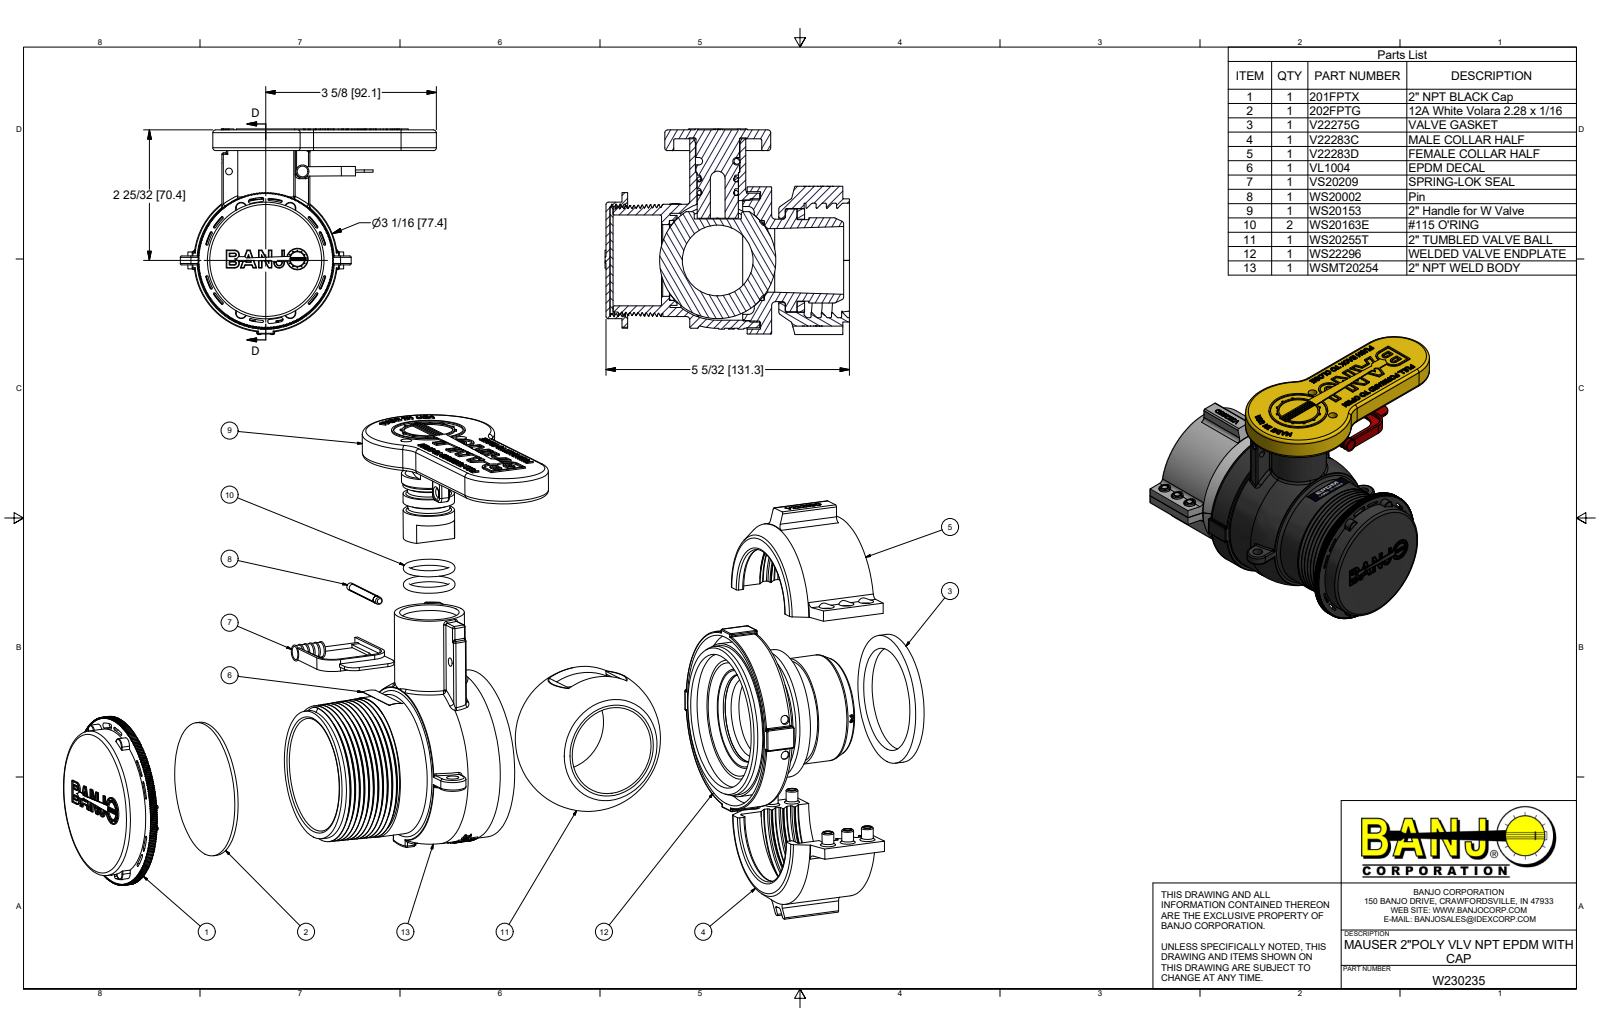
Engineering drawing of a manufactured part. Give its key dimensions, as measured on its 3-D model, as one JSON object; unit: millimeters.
{"part_name": "W230235; WSMT20254; WSMT20254X; V22275G (+8 more)", "step_written_by": "Autodesk Inventor 2018 (AUTOMOTIVE_DESIGN)", "units": "millimeters", "bodies": {"solids": 16, "faces": 3810, "planar": 1882, "cylindrical": 936, "other": 992}, "overall_size": [1020.5, 138.2, 110.9], "volume_mm3": 320000, "surface_area_mm2": 326900, "round_holes": [[5.3, 6], [6.5, 6], [3.7, 2], [3.8, 2], [4.8, 2], [5.3, 2], [38.1, 2], [4, 1], [7.8, 1], [7.9, 1], [11.1, 1], [21.3, 1]], "round_bosses_or_shafts": [[5.1, 6], [77.4, 1], [74.2, 1], [73.2, 1], [72.6, 1], [66.5, 1], [66.4, 1], [64.8, 1]], "partial_cylinders_radius": [[0.8, 68], [0.4, 24], [2.3, 10], [1.5, 4], [3, 4], [6.4, 4], [0.3, 3], [1.8, 3]], "face_to_face_distances": [1.6, 2.2, 4.8, 3.8, 85.6, 87.2, 89.4, 6.4, 0.5, 13.7], "hole_center_spacings": [73.2, 72.6, 9.5, 9.5, 19.1, 26.6, 41.5, 51.9]}
